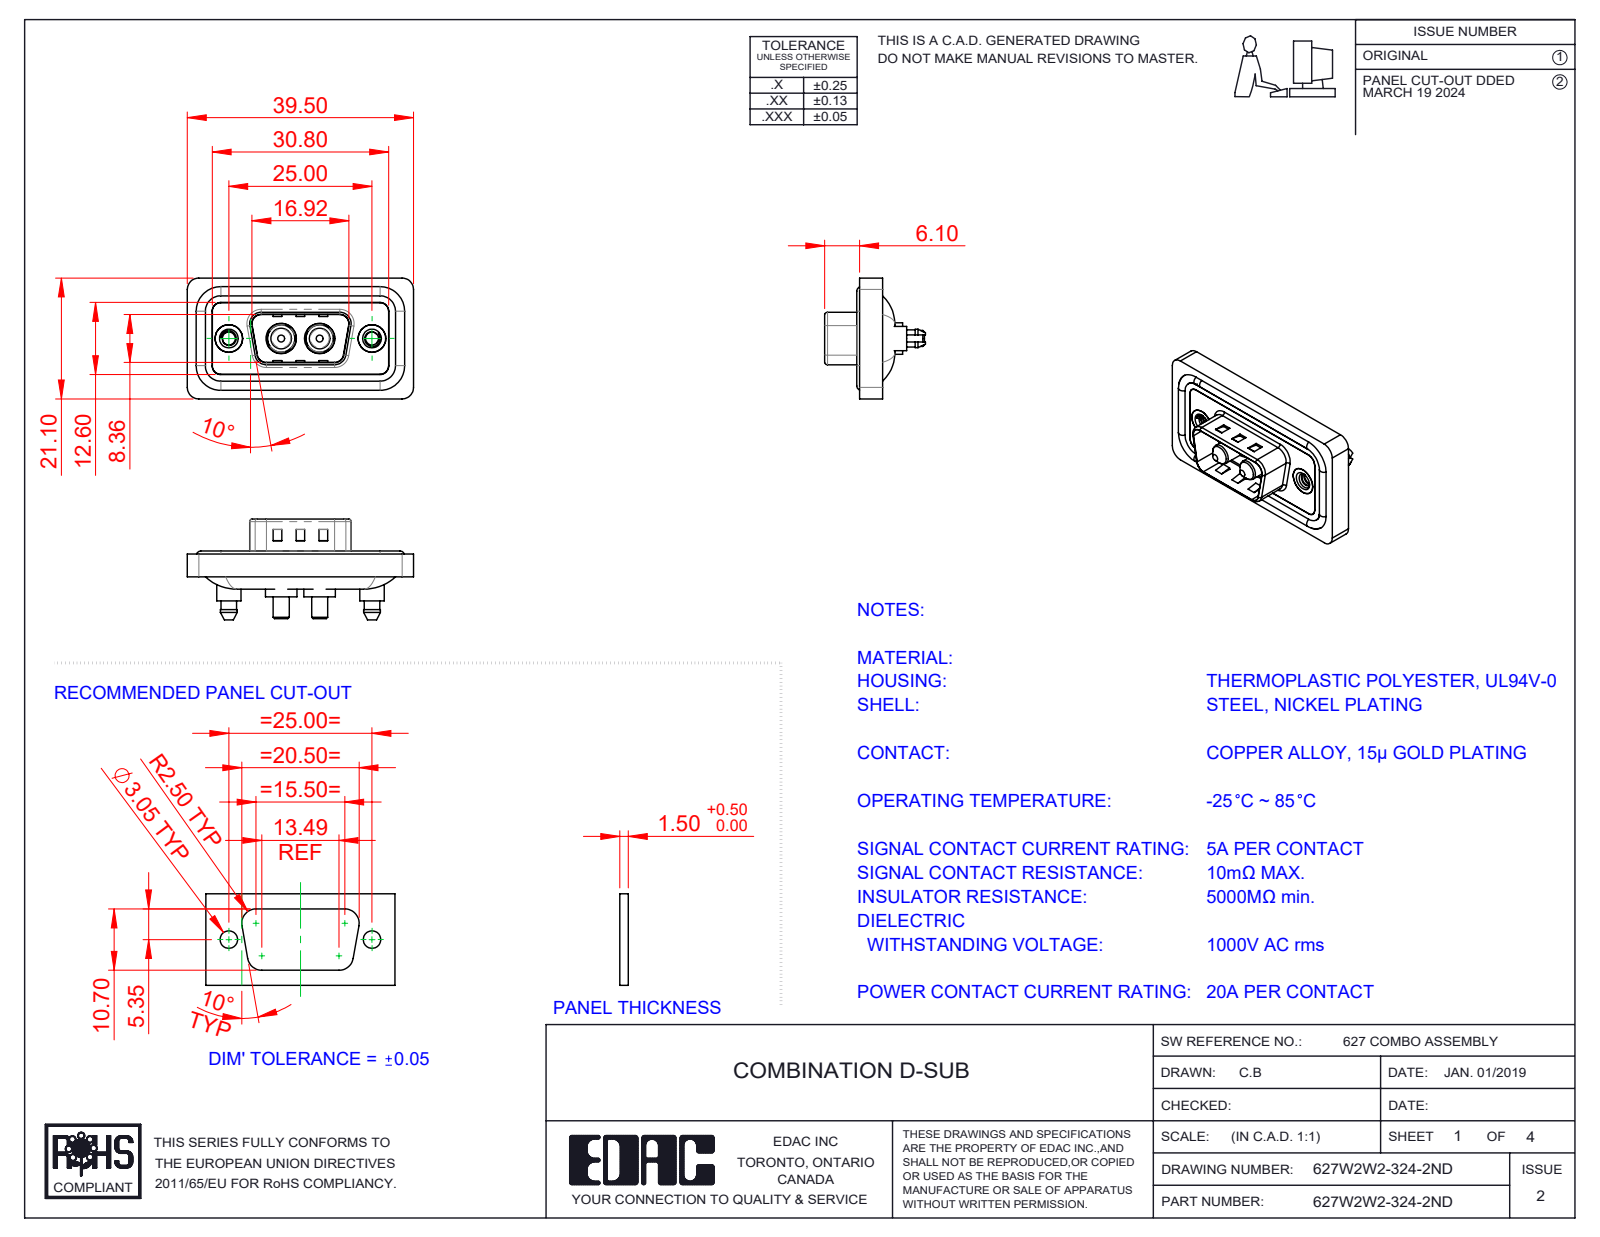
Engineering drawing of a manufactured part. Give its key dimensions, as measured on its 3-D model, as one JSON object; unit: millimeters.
{"part_name": "Power Pin_20A S; 627Combo Shell Front_09 Contacts; 627Combo Threaded Boardlock_5; 627W2W2-324-2ND (+4 more)", "step_written_by": "SolidWorks 2023 (CONFIG_CONTROL_DESIGN)", "units": "millimeters", "bodies": {"solids": 11, "faces": 547, "planar": 181, "cylindrical": 258, "other": 108}, "overall_size": [39.5, 21.1, 17.6], "volume_mm3": 4595, "surface_area_mm2": 7320, "round_holes": [[2.26, 2], [4, 2], [4.8, 2], [4.85, 2], [5, 2], [5.3, 2]], "round_bosses_or_shafts": [[1.6, 4], [5.5, 2], [5.4, 2], [5.2, 2], [4.9, 2], [4.75, 2], [4.25, 2], [3.75, 2]], "partial_cylinders_radius": [[1.5, 24], [2, 18], [1.6, 10], [0.5, 8], [0.25, 4], [0.6, 4], [0.65, 4], [0.9, 4]], "face_to_face_distances": [0.4, 1.1, 2.9, 3.1, 0.5, 1.6, 1.5, 4, 0.7, 2.5], "hole_center_spacings": [9.14, 15.86, 6.72, 25]}
